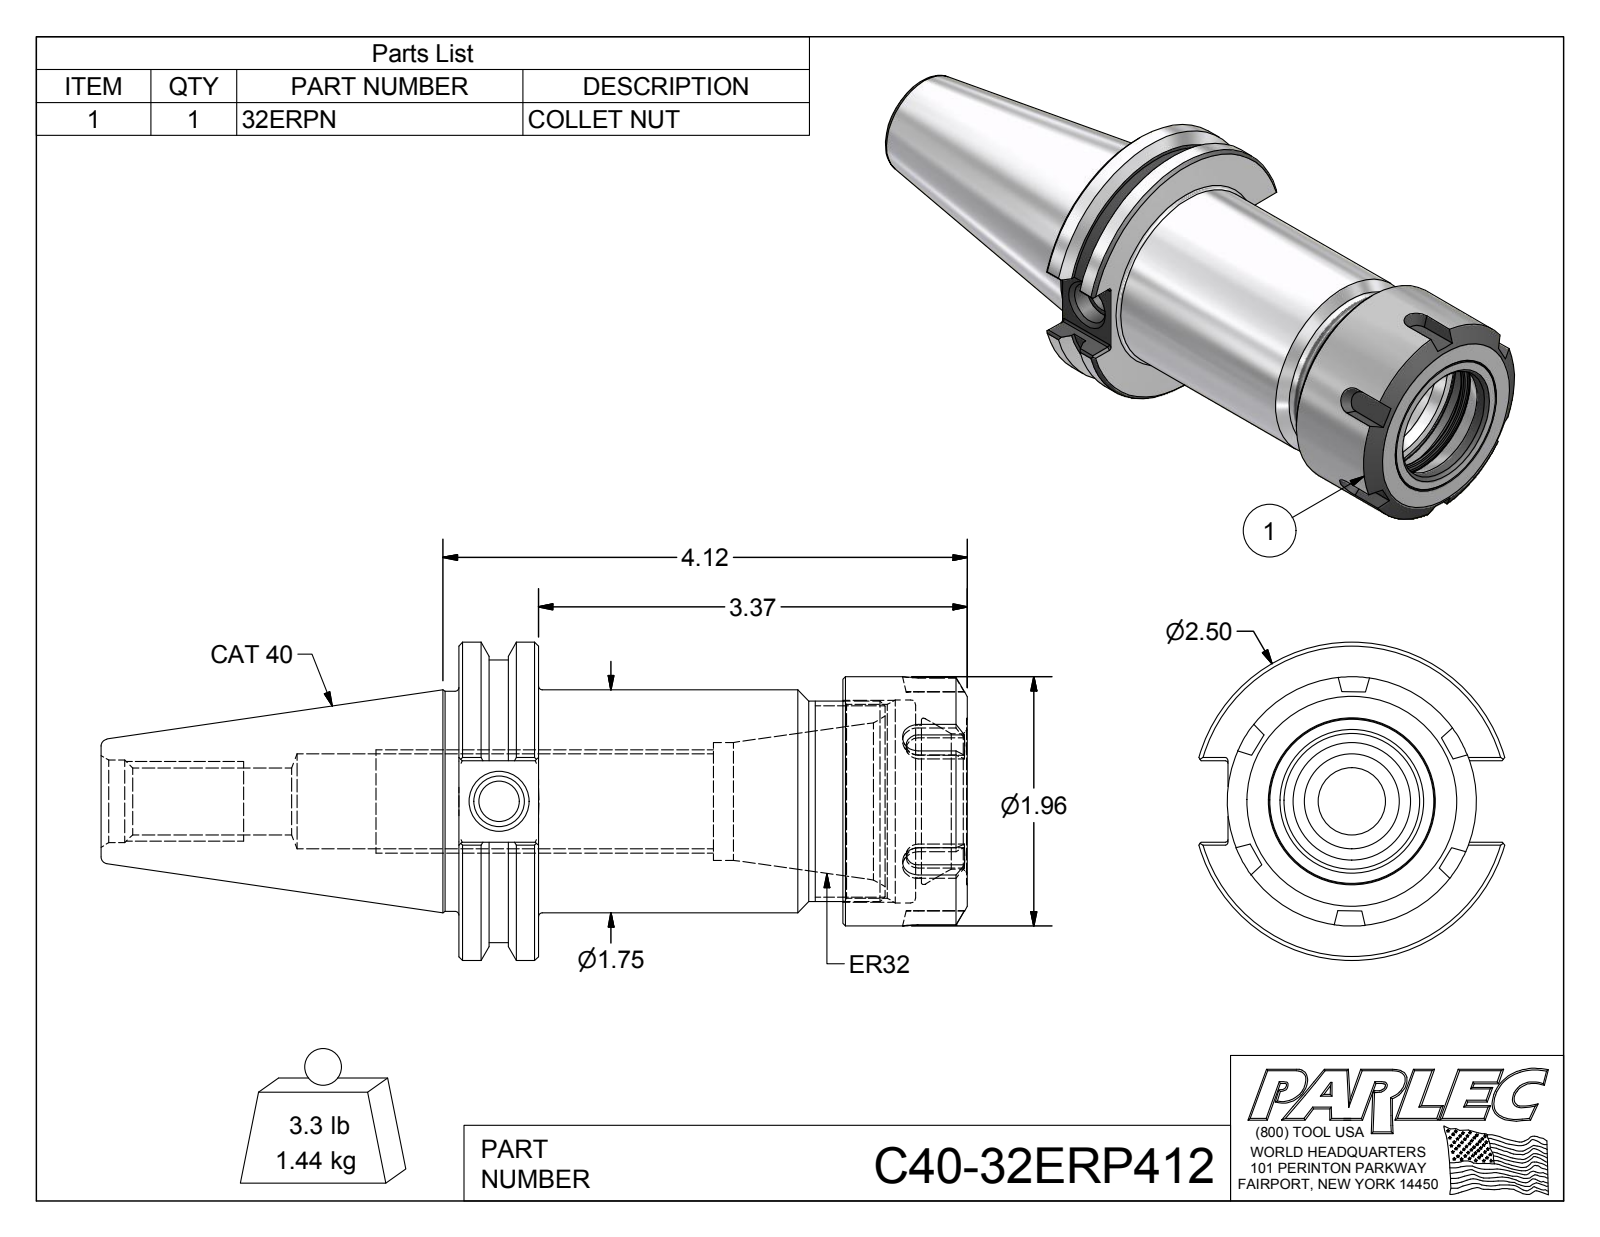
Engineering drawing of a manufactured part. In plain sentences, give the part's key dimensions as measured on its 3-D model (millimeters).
The part is named "C40-32ERP412; C40-32ER4-1; 32ERPN". Its 3-D file was written by "Autodesk Inventor 2012 (AUTOMOTIVE_DESIGN)". It is 2 solids with 129 faces: 55 planar, 33 cylindrical and 41 other. Overall it measures 172.9 by 63.5 by 61 millimeters. Its volume is 187 800 cubic millimeters and its surface area 44 100 square millimeters. Round holes: 1 of diameter 8, 1 of diameter 10.1, 1 of diameter 13.4, 1 of diameter 16.5, 1 of diameter 18.9, 1 of diameter 23.5, 1 of diameter 27, 1 of diameter 30.5, 1 of diameter 33.1, 1 of diameter 38.7, 1 of diameter 40.5. Round bosses or shafts: 1 of diameter 63.5, 1 of diameter 56.4, 1 of diameter 49.7, 1 of diameter 44.5, 1 of diameter 43.9, 1 of diameter 40. Partial cylindrical surfaces (rounded edges, fillets, slot ends): 12 of radius 0.5. The main face-to-face distances are 15.9, 101.5, 85.6, 76.6, 60.8, 24.8, 91.1, 75.3, 14.5, 10.3.
